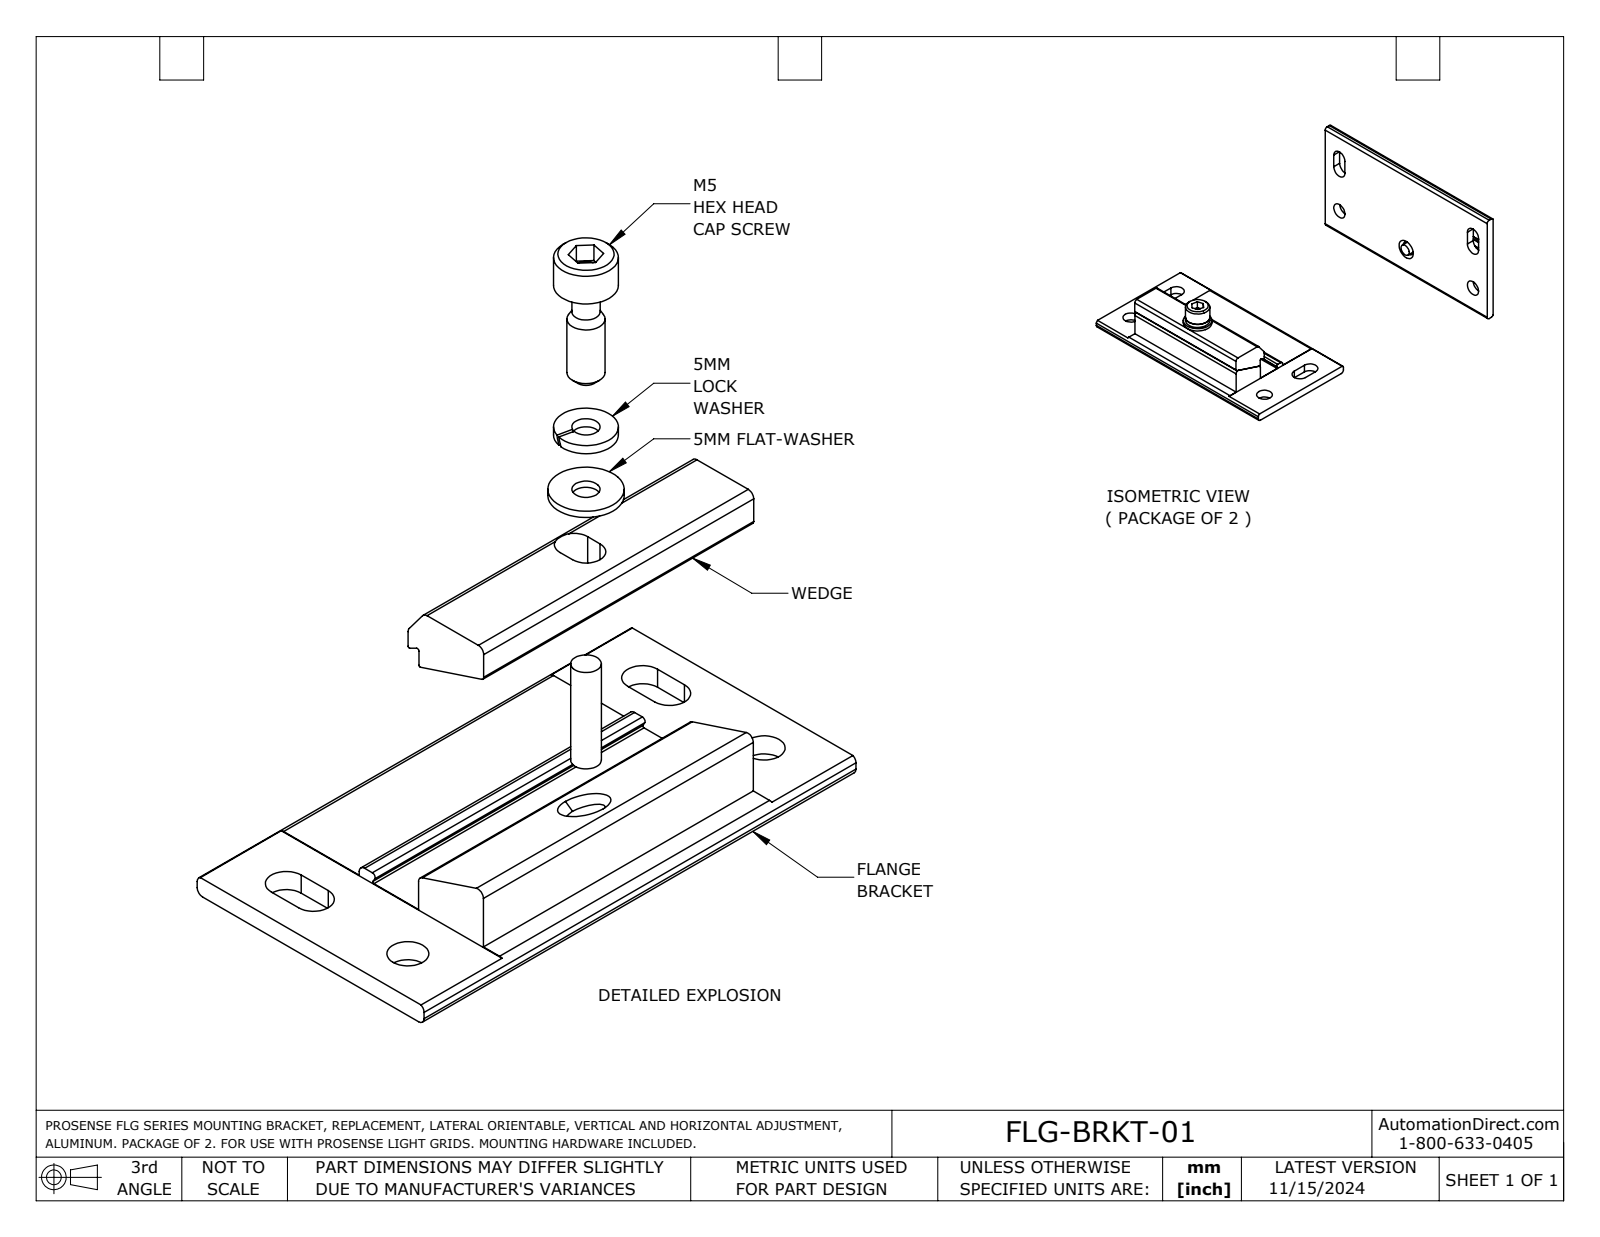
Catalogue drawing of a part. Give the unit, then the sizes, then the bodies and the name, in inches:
Units: inches
Overall size (bounding box): 7.874 × 5.413 × 1.654
Round holes (diameter × count): ⌀0.217 ×8, ⌀0.146 ×4, ⌀0.197 ×4
Round bosses / shafts (diameter × count): ⌀0.394 ×4, ⌀0.335 ×4, ⌀0.158 ×2, ⌀0.158 ×2
Partial cylindrical surfaces — rounded edges, fillets, slot ends (radius × count): R0.039 ×20, R0.108 ×16, R0.1 ×8, R0.008 ×6, R0.02 ×4, R0.012 ×2
Main face-to-face distances: 0.118, 0.114, 0.676, 0.562, 0.558, 0.472, 4.724, 0.591, 2.559, 4.968
Hole centre spacings: 1.299, 4.724, 2.598, 3.425, 6.024, 2.126, 7.323
Volume: 4.595 in³ · Surface area: 72.66 in²
Bodies: 24 solids, 364 faces (204 planar, 132 cylindrical, 28 other)
Part name (STEP PRODUCT): FLG-BRKT-01
STEP written by: SolidWorks 2023 (AUTOMOTIVE_DESIGN)
